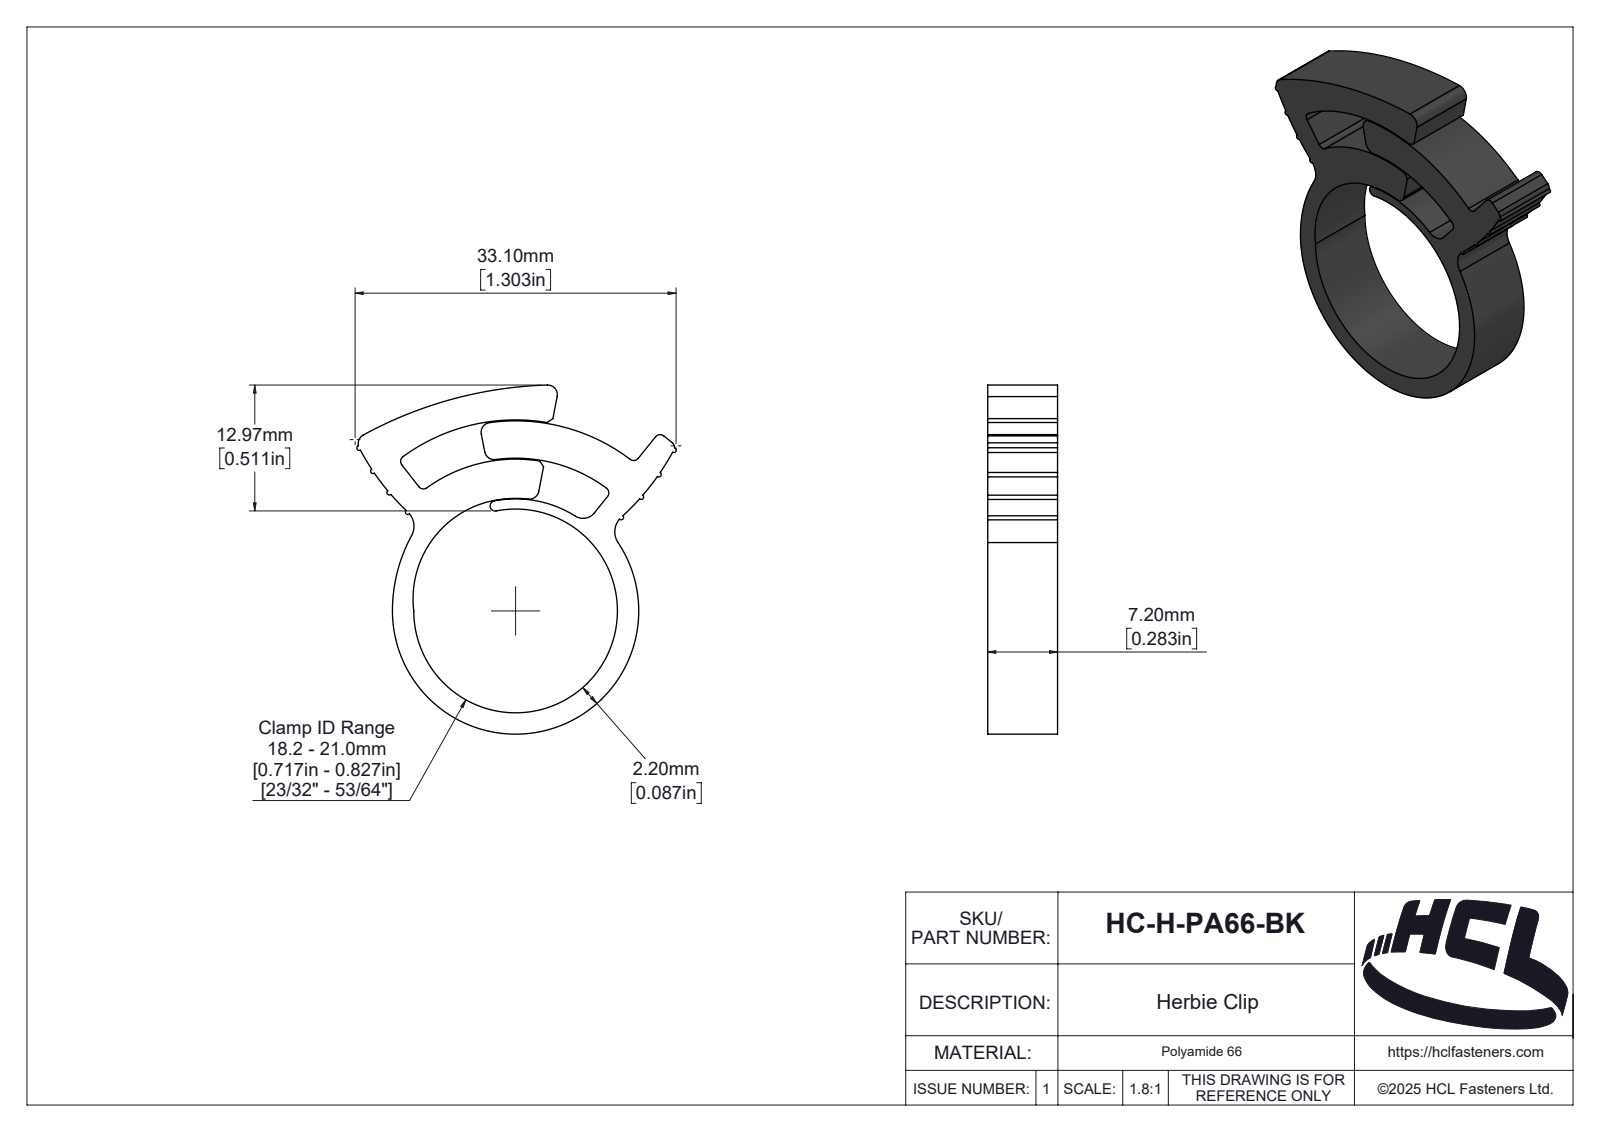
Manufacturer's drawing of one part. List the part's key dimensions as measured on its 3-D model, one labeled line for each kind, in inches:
Part name (STEP PRODUCT): HC-H-PA66-BK
STEP written by: SolidWorks 2025 (AUTOMOTIVE_DESIGN)
Units: inches
Bodies: 1 solid, 162 faces (13 planar, 100 cylindrical, 49 other)
Overall size (bounding box): 1.417 × 1.297 × 0.283
Volume: 0.159 in³ · Surface area: 4.132 in²
Partial cylindrical surfaces — rounded edges, fillets, slot ends (radius × count): R0.01 ×8, R0.024 ×6, R0.039 ×5, R0.079 ×2, R0.007 ×1, R0.021 ×1, R0.026 ×1, R0.033 ×1
Main face-to-face distances: 0.283
